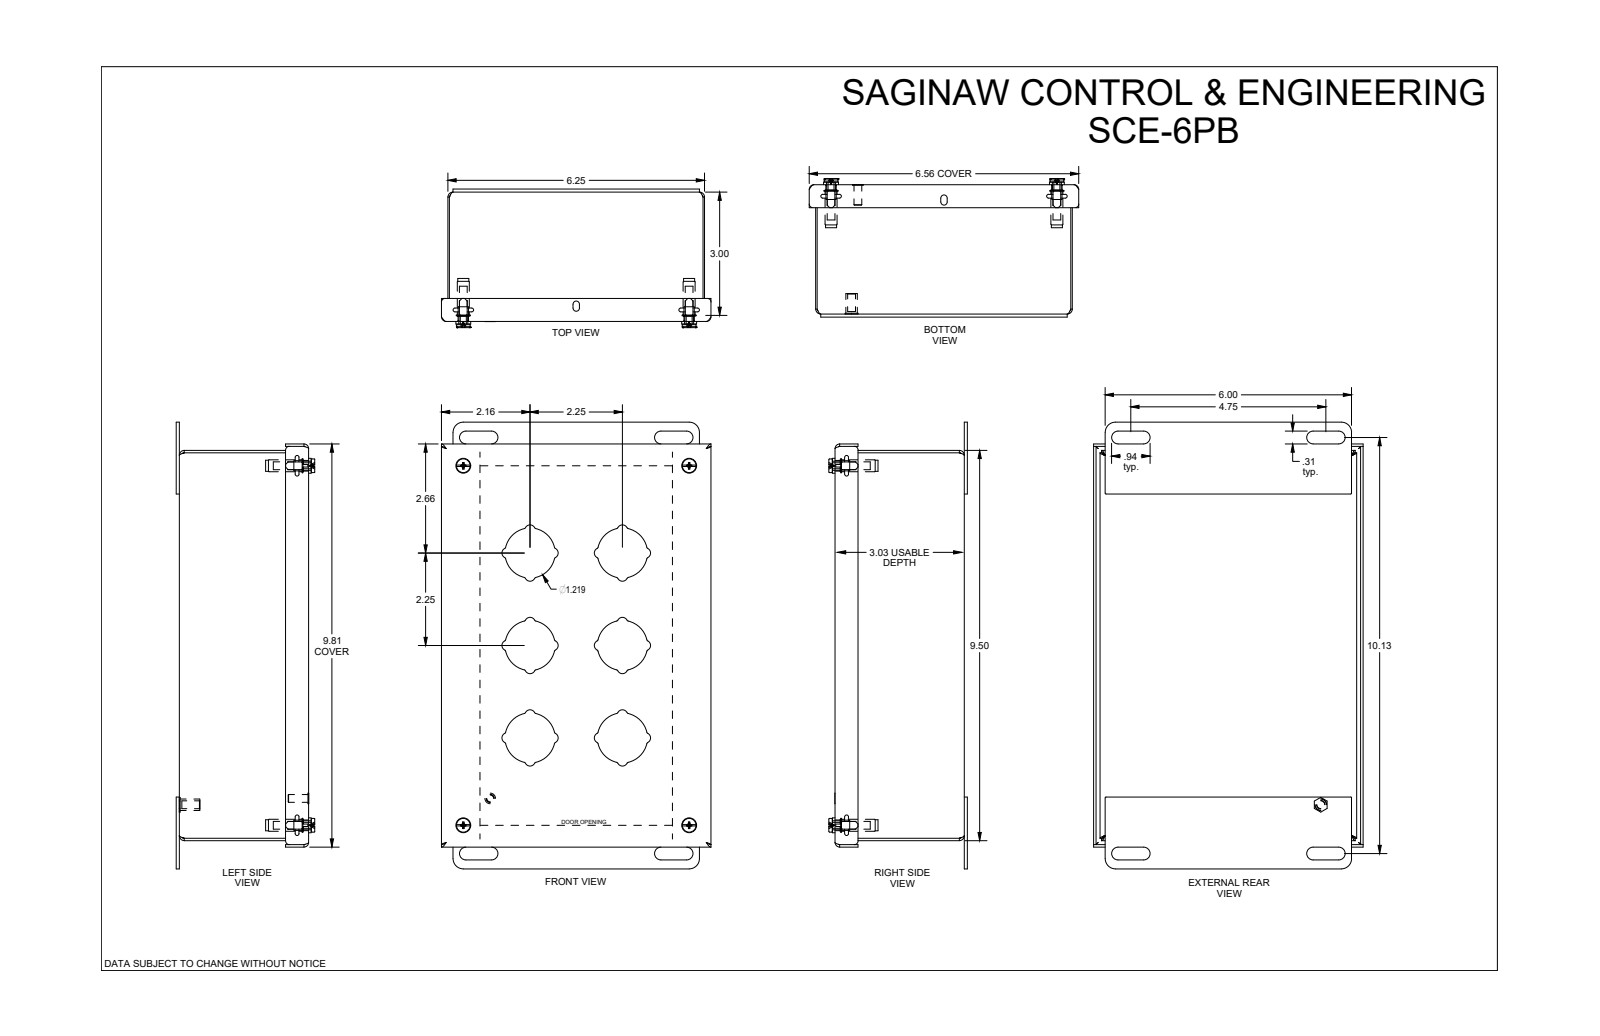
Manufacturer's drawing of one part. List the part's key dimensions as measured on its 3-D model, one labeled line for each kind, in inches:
Part name (STEP PRODUCT): SCE-6PB
STEP written by: SolidWorks 2021 (AUTOMOTIVE_DESIGN)
Units: inches
Bodies: 3 solids, 514 faces (154 planar, 276 cylindrical, 84 other)
Overall size (bounding box): 10.875 × 6.563 × 3.286
Volume: 16.31 in³ · Surface area: 515.7 in²
Round holes (diameter × count): ⌀0.19 ×5, ⌀0.22 ×4, ⌀0.25 ×4, ⌀0.266 ×4, ⌀0.317 ×4
Round bosses / shafts (diameter × count): ⌀0.362 ×4, ⌀0.34 ×4, ⌀0.292 ×4, ⌀0.27 ×4, ⌀0.26 ×4, ⌀0.28 ×1, ⌀0.256 ×1, ⌀0.188 ×1
Partial cylindrical surfaces — rounded edges, fillets, slot ends (radius × count): R0.04 ×48, R0.125 ×24, R0.06 ×20, R0.015 ×8, R0.115 ×8, R0.156 ×8, R0.245 ×8, R0.609 ×6
Main face-to-face distances: 0.06, 3.088, 3.028, 6.19, 3.148, 9.44, 0.156, 6.25, 6.13, 0.075
Hole centre spacings: 10.335, 5.5, 5.5, 8.75, 8.75, 10.335, 0.7, 0.707
